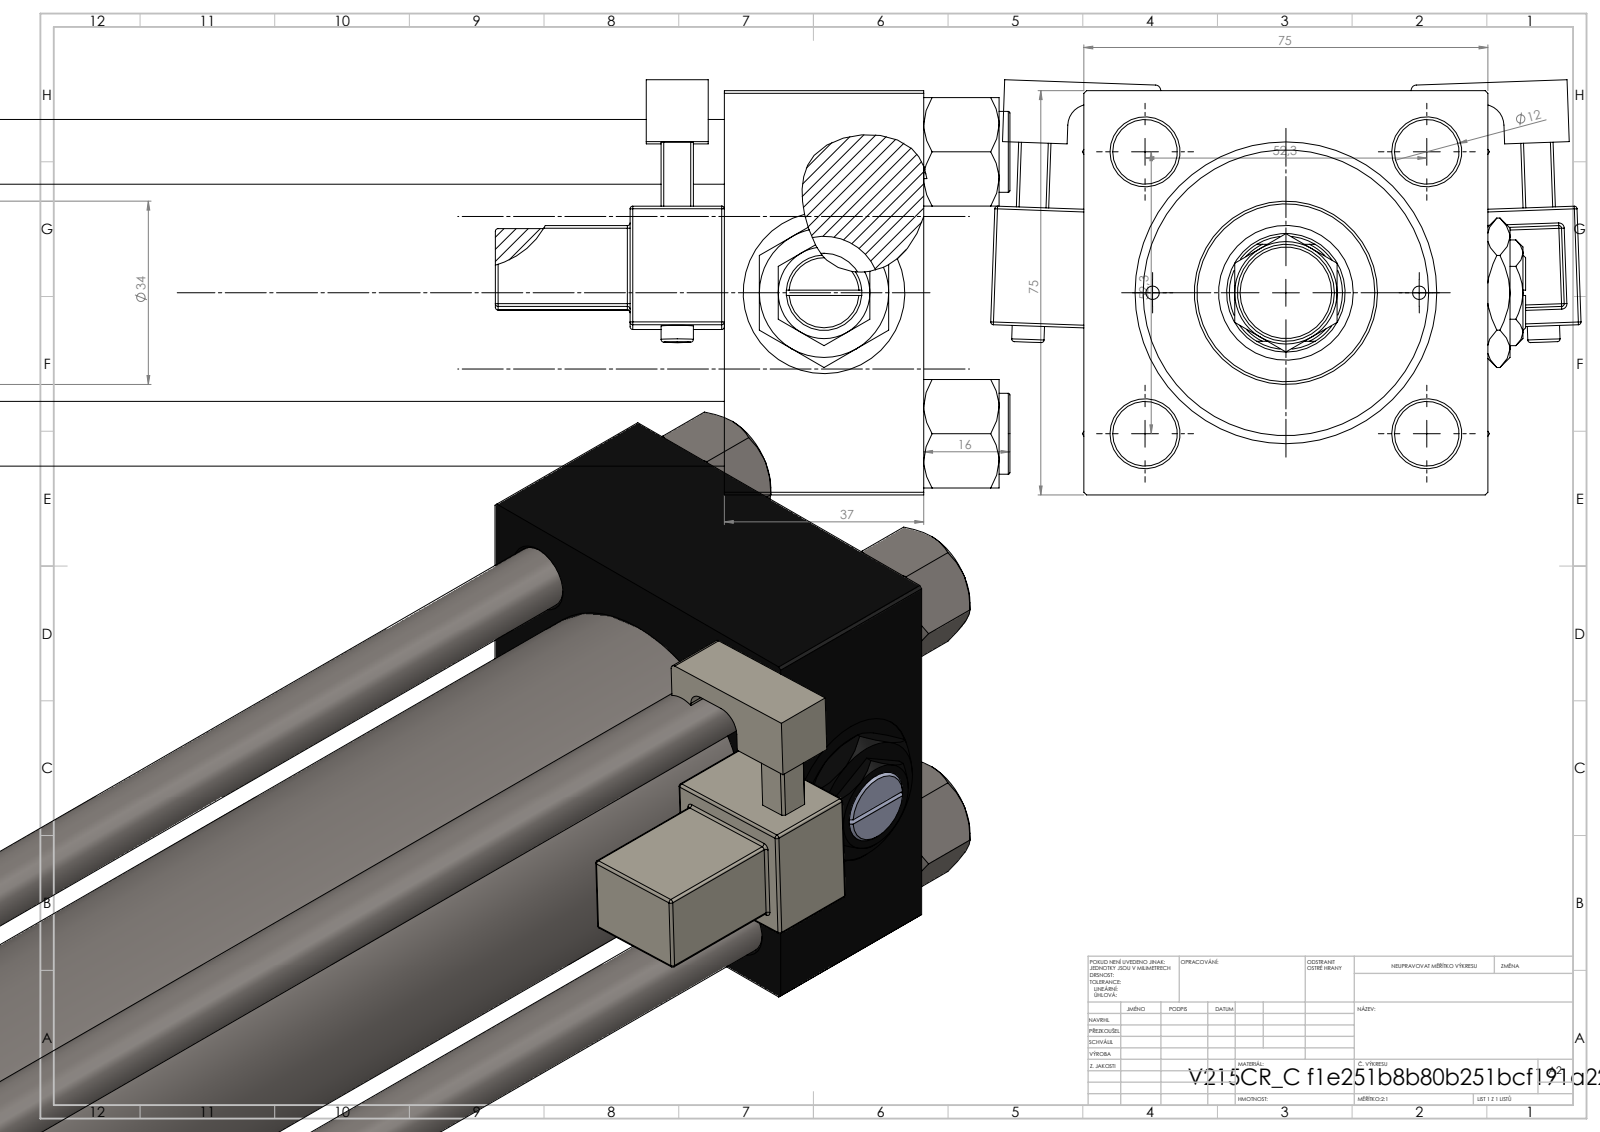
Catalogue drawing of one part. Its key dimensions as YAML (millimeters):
part_name: "Zatka_pro_OIL_PORT; NUT_M5_C; V215CR_VCP_C; V215CR_C_TYCINKA (+4 more)"
step_written_by: "SolidWorks 2019 (CONFIG_CONTROL_DESIGN)"
units: millimeters
bodies: {solids: 16, faces: 1461, planar: 649, cylindrical: 166, other: 646}
overall_size: [508, 109.57, 77.03]
volume: 1074000
surface_area: 321625
round_holes:
  - {diameter: 12, count: 4}
  - {diameter: 2.5, count: 2}
  - {diameter: 7, count: 2}
  - {diameter: 20.96, count: 2}
  - {diameter: 30, count: 2}
  - {diameter: 10.5, count: 1}
  - {diameter: 22, count: 1}
  - {diameter: 25, count: 1}
  - {diameter: 41, count: 1}
  - {diameter: 50, count: 1}
  - {diameter: 53, count: 1}
round_bosses_or_shafts:
  - {diameter: 15, count: 4}
  - {diameter: 6, count: 2}
  - {diameter: 56, count: 1}
  - {diameter: 34, count: 1}
  - {diameter: 18, count: 1}
  - {diameter: 11, count: 1}
partial_cylinders:
  - {radius: 0.5, count: 48}
  - {radius: 1, count: 2}
  - {radius: 2.5, count: 2}
  - {radius: 4, count: 2}
  - {radius: 10.5, count: 1}
face_to_face_distances: [75, 37, 434, 397, 375, 338, 59, 405.3, 368.3, 30.3]
hole_center_spacings: [26.19, 36.98, 52.3, 57.22, 24.75, 73.96, 49.5, 373.5]
